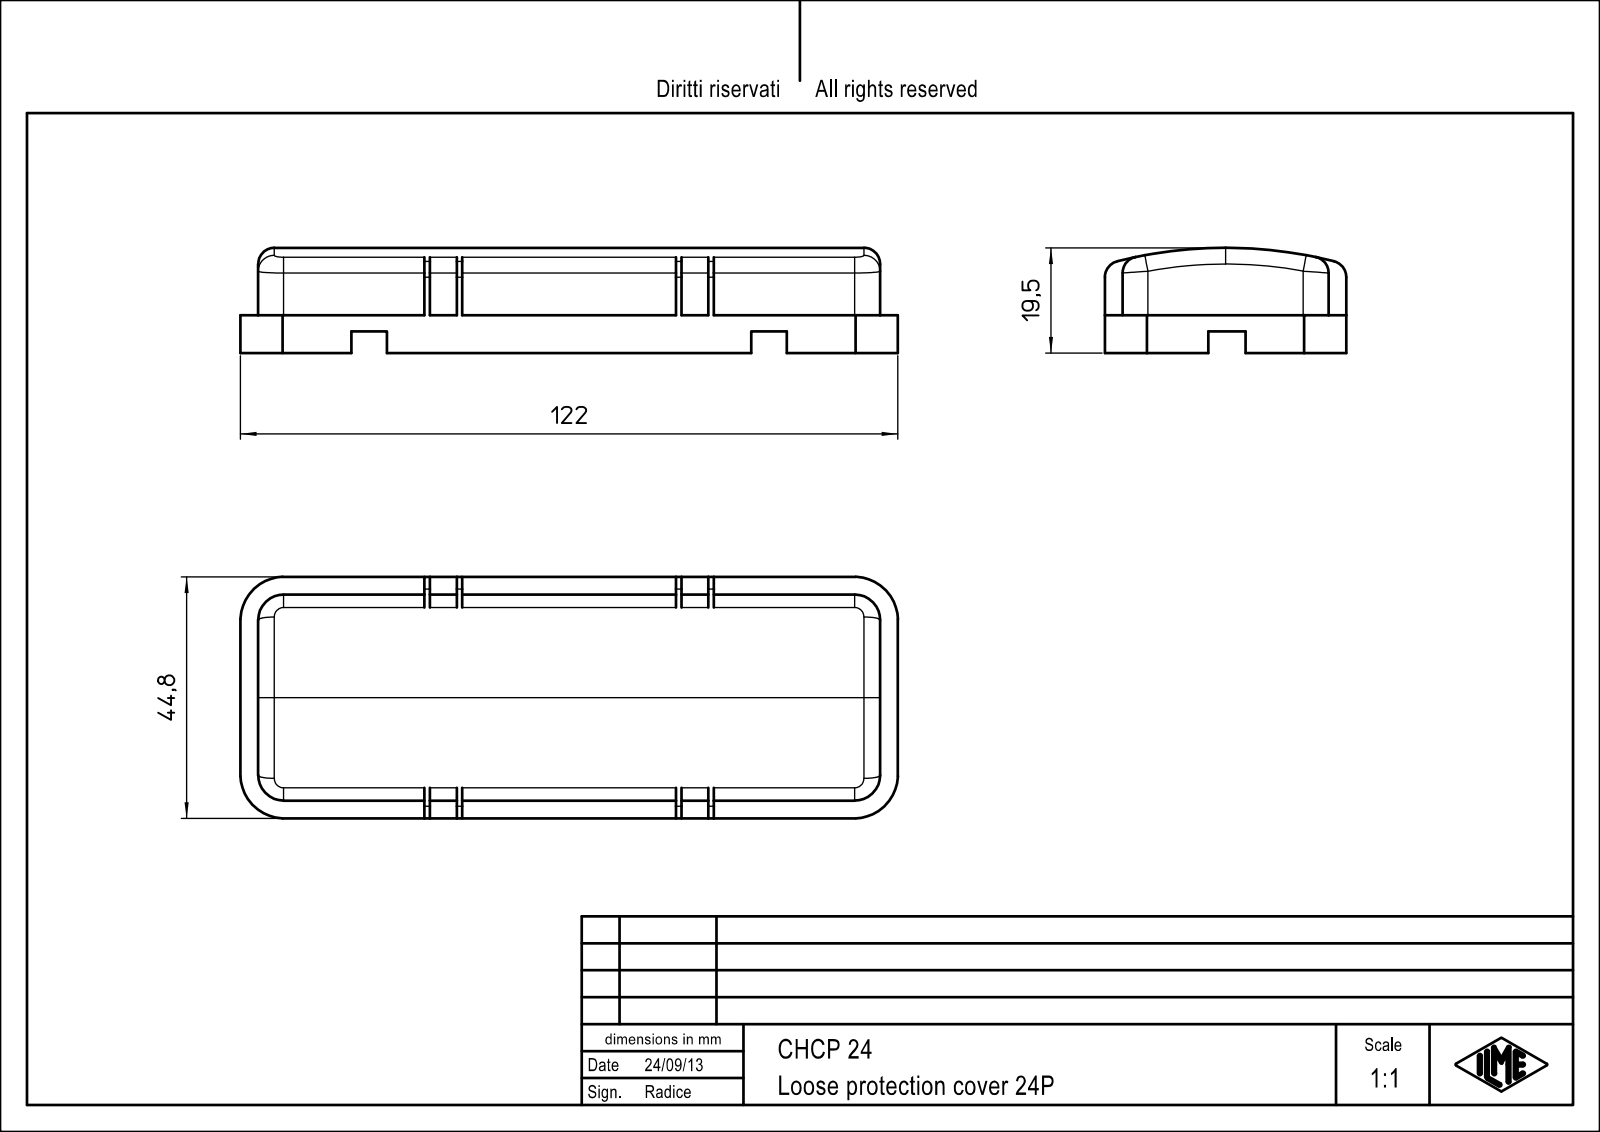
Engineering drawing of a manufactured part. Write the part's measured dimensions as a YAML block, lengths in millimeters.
part_name: "CHCP_24"
step_written_by: "Creo Elements/Direct Modeling 18.0B 02-Dec-2011 (C) Parametric Technology GmbH (AUTOMOTIVE_DESIGN)"
units: millimeters
bodies: {solids: 1, faces: 185, planar: 104, cylindrical: 64, other: 17}
overall_size: [122, 44.8, 19.5]
volume: 10594
surface_area: 21205
partial_cylinders:
  - {radius: 0.33, count: 15}
  - {radius: 3, count: 8}
  - {radius: 4.7, count: 4}
  - {radius: 7.2, count: 4}
  - {radius: 8.11, count: 4}
  - {radius: 0.17, count: 2}
  - {radius: 81, count: 2}
  - {radius: 82, count: 2}
face_to_face_distances: [1.12, 4.4, 3.28, 37.12, 0.9, 3.5, 40.4, 41.52, 2.38, 1]
